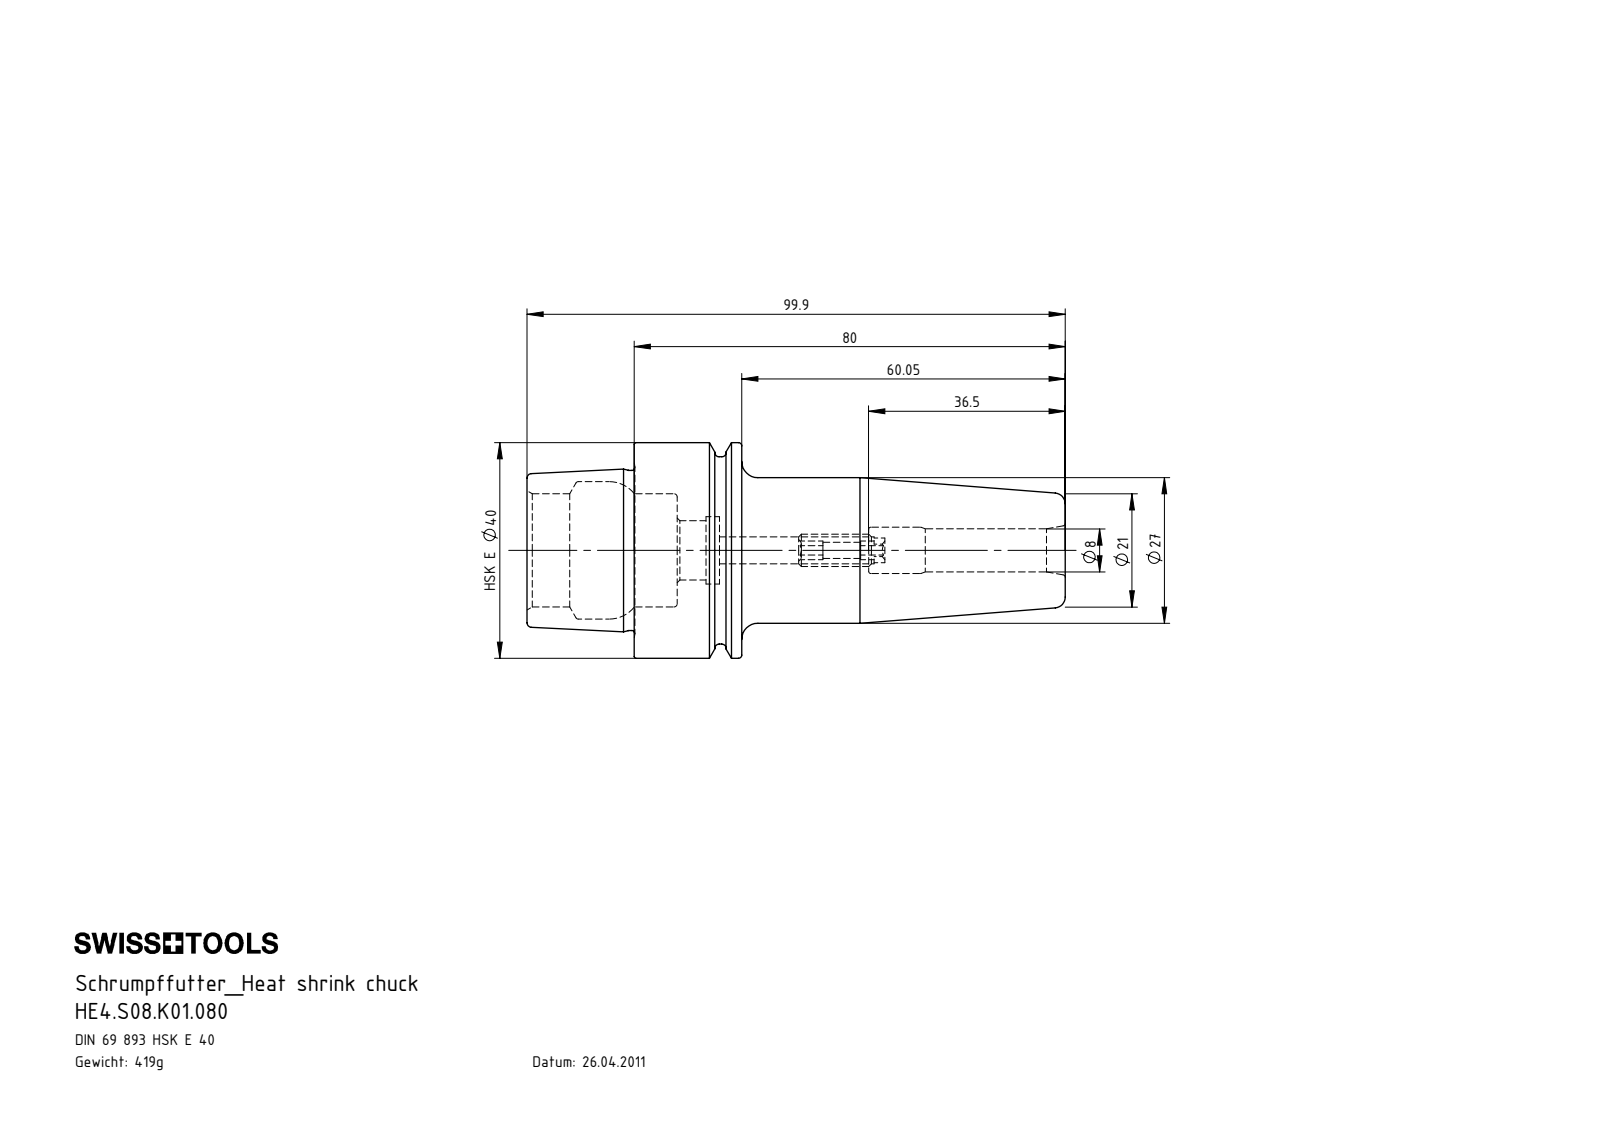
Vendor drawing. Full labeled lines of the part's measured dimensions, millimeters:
Part name (STEP PRODUCT): HE4-S08.K01.080; ERU-AN2.K01.016_A; HE4-S08.K01.080_B_Fertigbearbeitung
STEP written by: SolidWorks 2012 (AUTOMOTIVE_DESIGN)
Units: millimetres
Bodies: 2 solids, 131 faces (43 planar, 32 cylindrical, 56 other)
Overall size (bounding box): 99.9 × 40 × 40
Volume: 53 439 mm³ · Surface area: 15 600 mm²
Round holes (diameter × count): ⌀3 ×1, ⌀5 ×1, ⌀8 ×1, ⌀8.6 ×1, ⌀11 ×1, ⌀12.5 ×1, ⌀21 ×1, ⌀25.5 ×1
Round bosses / shafts (diameter × count): ⌀40 ×1, ⌀34.75 ×1, ⌀29.71 ×1, ⌀27 ×1, ⌀6 ×1
Main face-to-face distances: 19.95, 7.95, 12, 19.9, 27.85, 39.85, 99.9, 80, 72.05, 60.05
